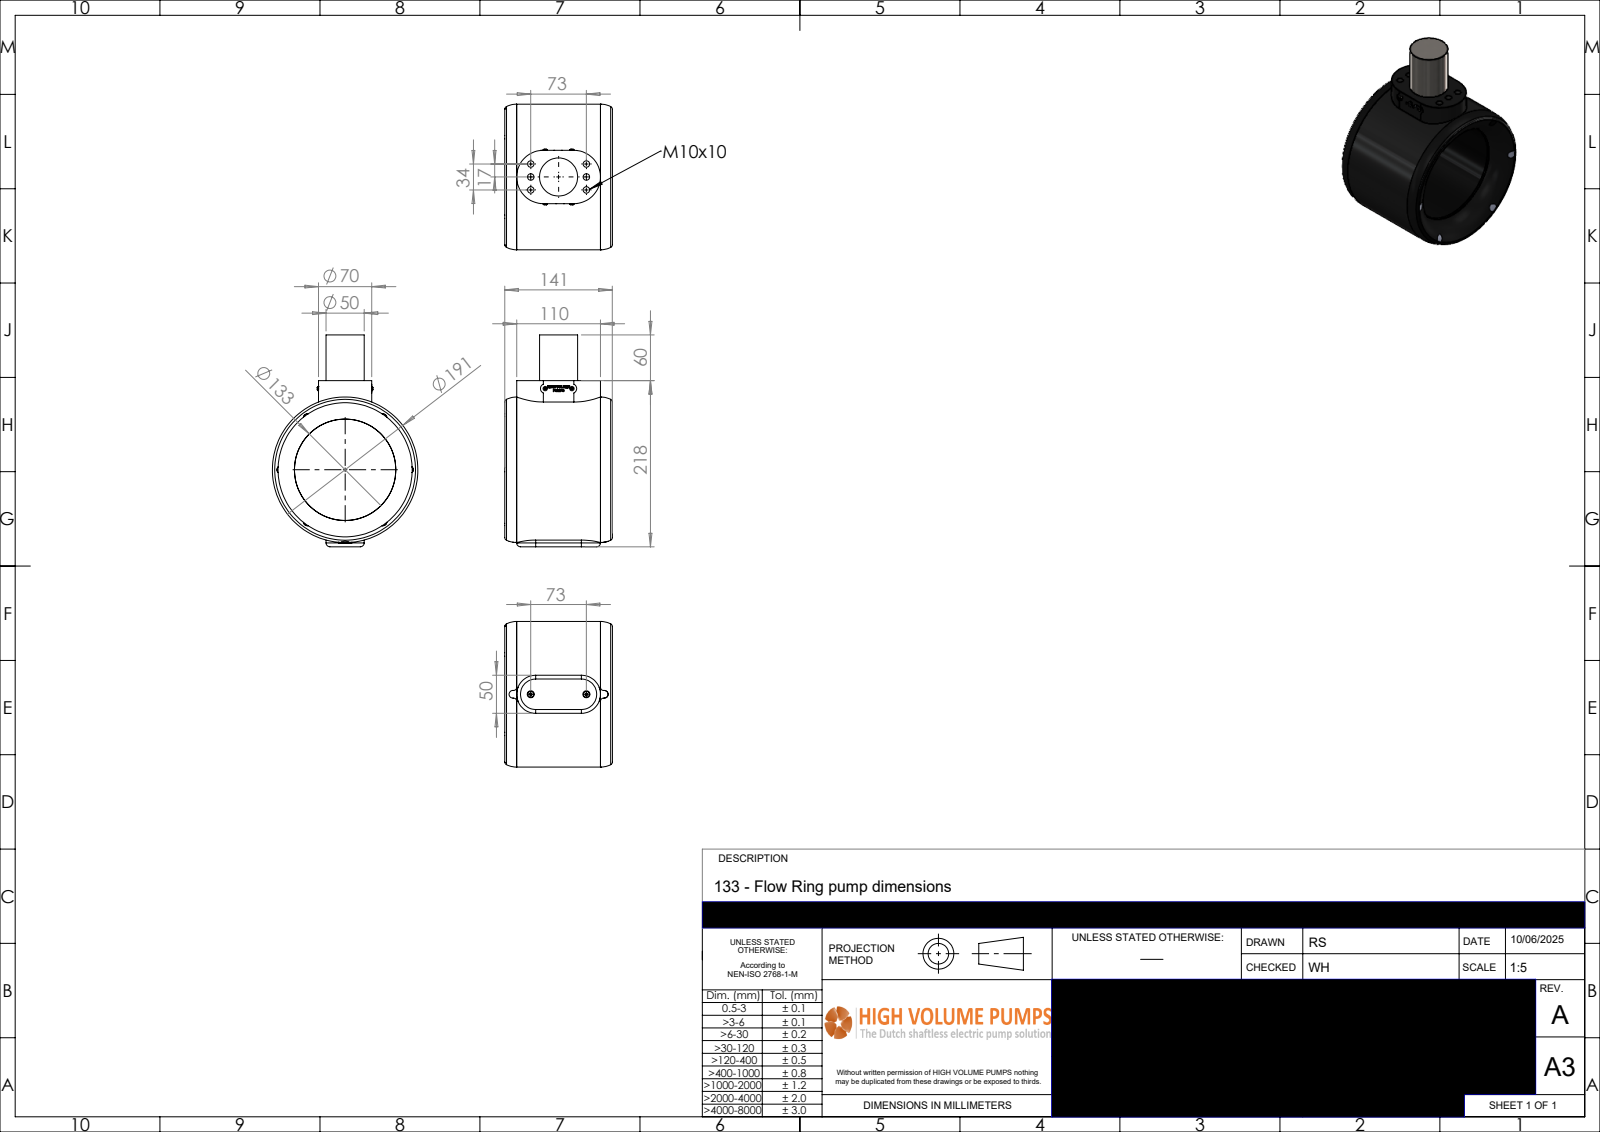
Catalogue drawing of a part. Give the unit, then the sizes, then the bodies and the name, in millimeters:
Units: millimetres
Overall size (bounding box): 278 × 191 × 141.23
Round holes (diameter × count): ⌀8.5 ×6, ⌀4.3 ×2, ⌀133 ×1, ⌀133.04 ×1
Round bosses / shafts (diameter × count): ⌀7.64 ×6, ⌀5.7 ×2, ⌀4 ×2, ⌀191 ×1, ⌀50 ×1
Partial cylindrical surfaces — rounded edges, fillets, slot ends (radius × count): R4 ×4, R5 ×4, R2.25 ×2, R6.25 ×2, R25 ×2, R35 ×2
Main face-to-face distances: 218, 60, 278, 70, 5, 10, 213, 273, 205.56, 200.56
Hole centre spacings: 17, 74.95, 73, 34, 80.53
Volume: 2 229 000 mm³ · Surface area: 181 651 mm²
Bodies: 1 solid, 652 faces (414 planar, 52 cylindrical, 186 other)
Part name (STEP PRODUCT): P-133-030-rev-A-FR
STEP written by: SolidWorks 2024 (AUTOMOTIVE_DESIGN)
